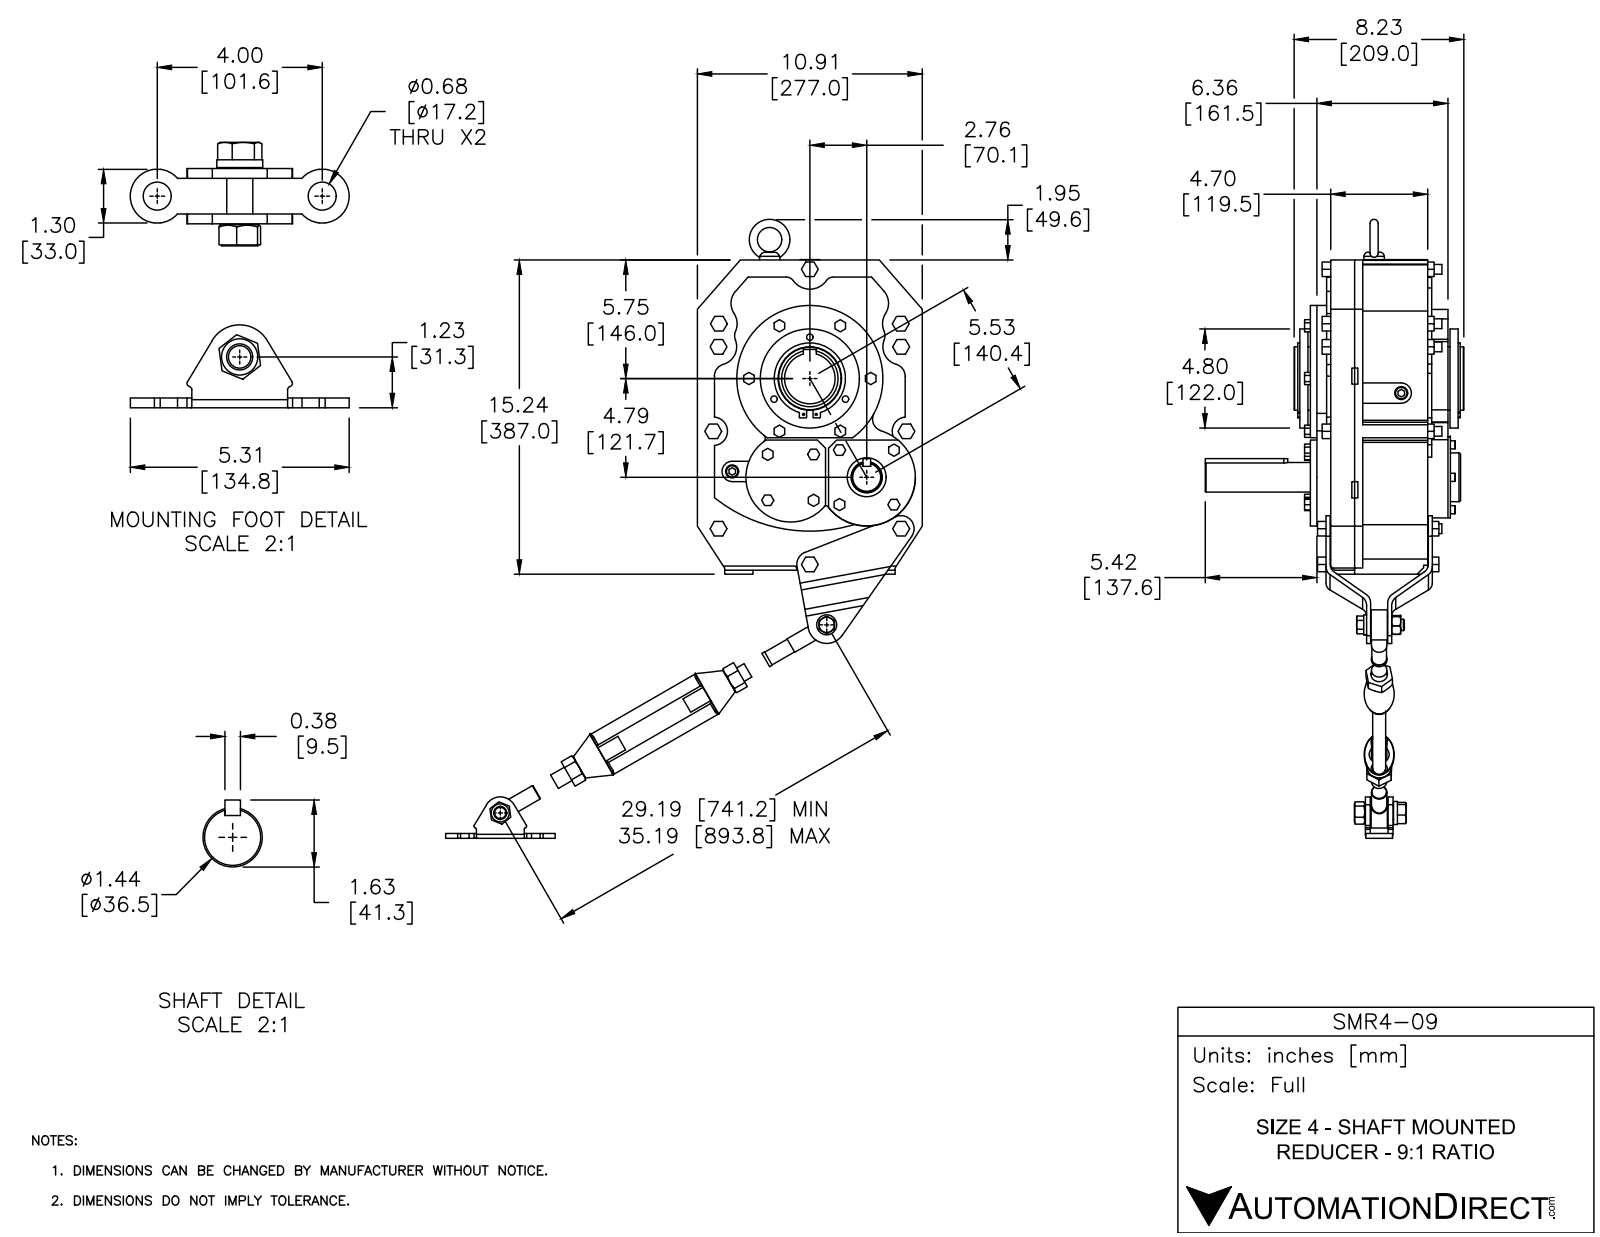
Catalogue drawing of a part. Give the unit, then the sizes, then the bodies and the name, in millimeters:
Units: millimetres
Overall size (bounding box): 809.5 × 669.1 × 318.5
Round holes (diameter × count): ⌀13 ×10, ⌀16 ×6, ⌀10.7 ×4, ⌀13.5 ×4, ⌀8 ×3, ⌀2.5 ×2, ⌀17.2 ×2, ⌀17.5 ×2, ⌀20 ×2, ⌀14 ×1, ⌀14.2 ×1, ⌀14.5 ×1
Round bosses / shafts (diameter × count): ⌀12 ×10, ⌀19.1 ×4, ⌀10 ×4, ⌀37 ×2, ⌀18.1 ×2, ⌀16 ×2, ⌀180 ×1, ⌀122 ×1
Partial cylindrical surfaces — rounded edges, fillets, slot ends (radius × count): R3 ×17, R10 ×11, R12.5 ×6, R15 ×6, R17.5 ×6, R22.5 ×6, R1 ×4, R2 ×4
Main face-to-face distances: 5, 46.5, 25, 144.5, 6, 20, 161.5, 149.5, 124.5, 8
Hole centre spacings: 79, 111.7, 50.8, 224, 260.8, 28.5, 32.7, 40.9
Volume: 13 980 000 mm³ · Surface area: 1 235 000 mm²
Bodies: 74 solids, 1270 faces (715 planar, 430 cylindrical, 125 other)
Part name (STEP PRODUCT): SMR4-09_REDUCER; SMR4-09; SMR4-TA; SMR4-TA_5 (+4 more)
STEP written by: SolidWorks 2016 (AUTOMOTIVE_DESIGN)
